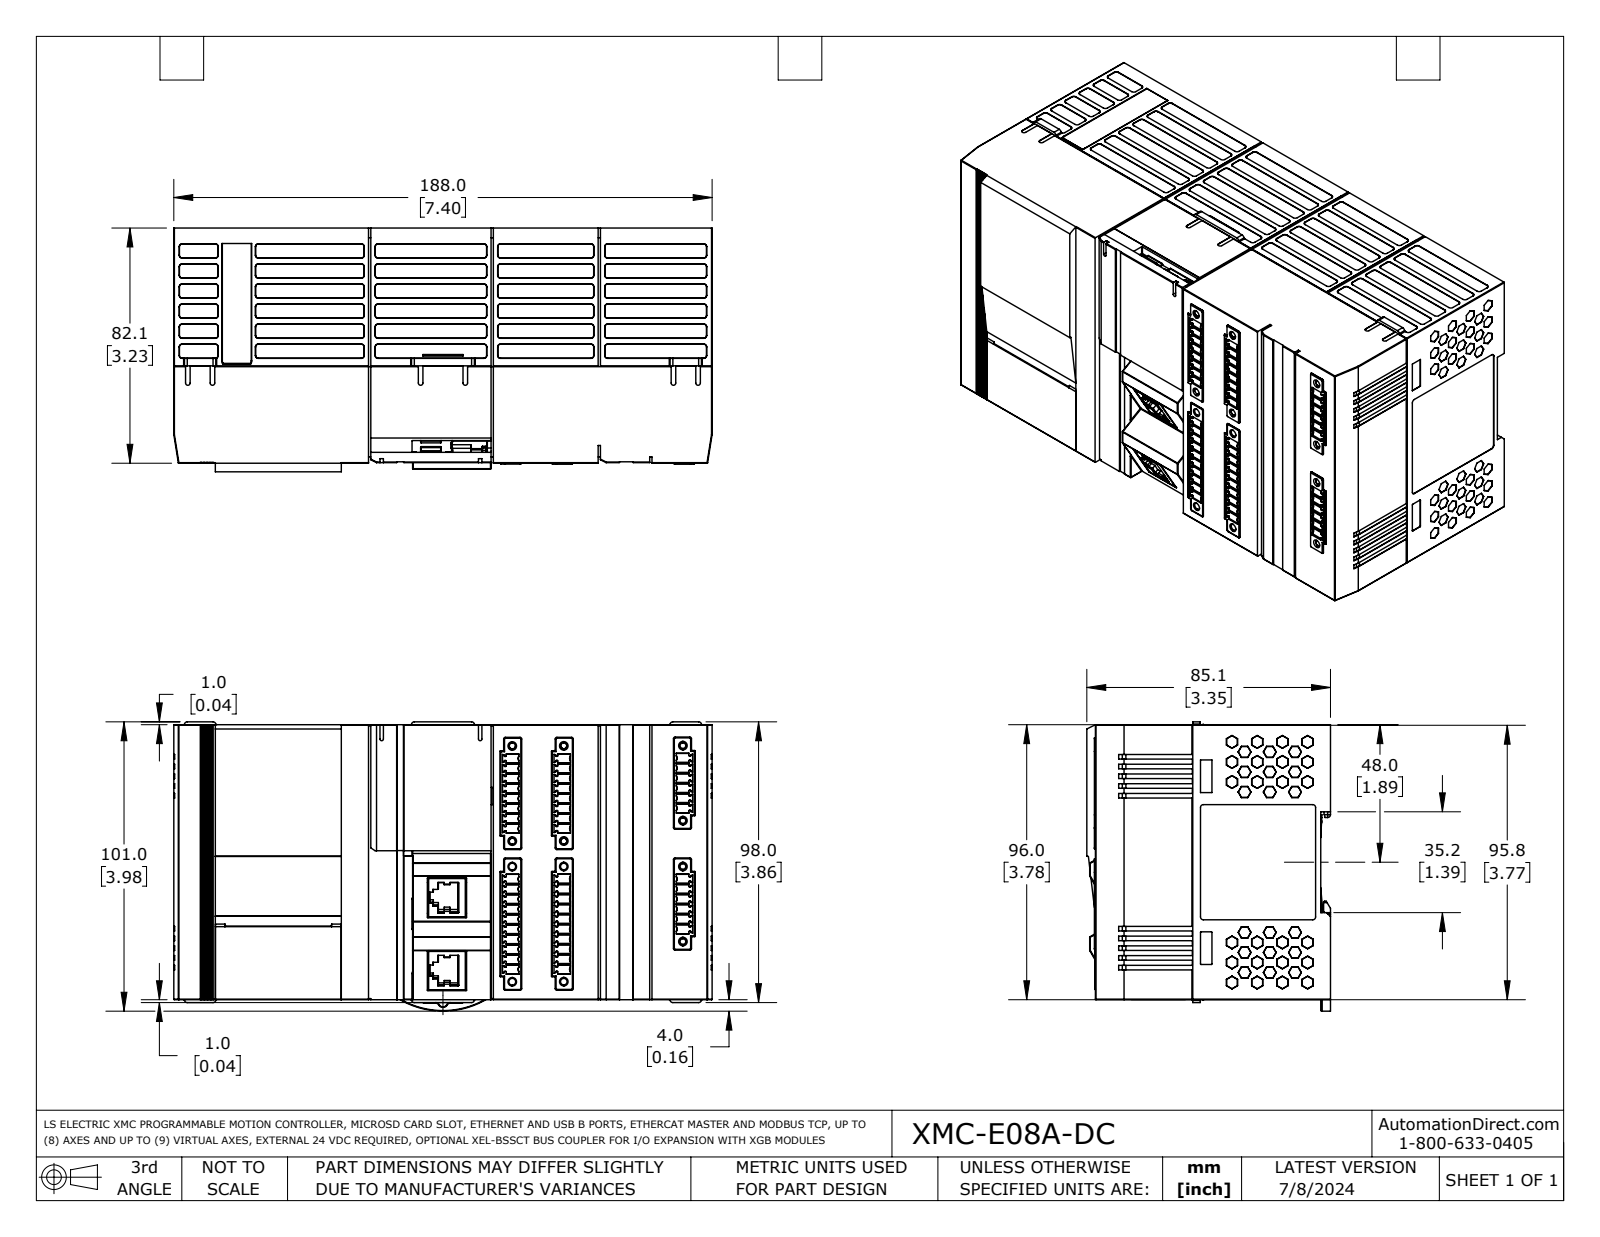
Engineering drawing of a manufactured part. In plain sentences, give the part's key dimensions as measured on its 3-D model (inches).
The part is named "XMC-E08A-DC". Its 3-D file was written by "SolidWorks 2021 (AUTOMOTIVE_DESIGN)". It is 1 solid with 4920 faces: 3175 planar, 1089 cylindrical and 656 other. Overall it measures 7.402 by 3.976 by 3.35 inches. Its volume is 87.08 cubic inches and its surface area 157 square inches. Round holes: 4 of diameter 0.079, 1 of diameter 0.083, 1 of diameter 0.098, 1 of diameter 0.134. Round bosses or shafts: 5 of diameter 0.209, 5 of diameter 0.118, 4 of diameter 0.079, 1 of diameter 0.205, 1 of diameter 0.157. Partial cylindrical surfaces (rounded edges, fillets, slot ends): 448 of radius 0.008, 144 of radius 0.02, 87 of radius 0.039, 46 of radius 0.012, 40 of radius 0.062, 27 of radius 0.024, 12 of radius 0.01, 7 of radius 0.031. The main face-to-face distances are 3.777, 3.78, 3.098, 3.775, 7.398, 3.232, 7.402, 0.134, 3.091, 3.224. The hole center spacings are 0.465, 0.631, 1.031, 1.031, 1.106, 1.661, 1.662, 1.699.
